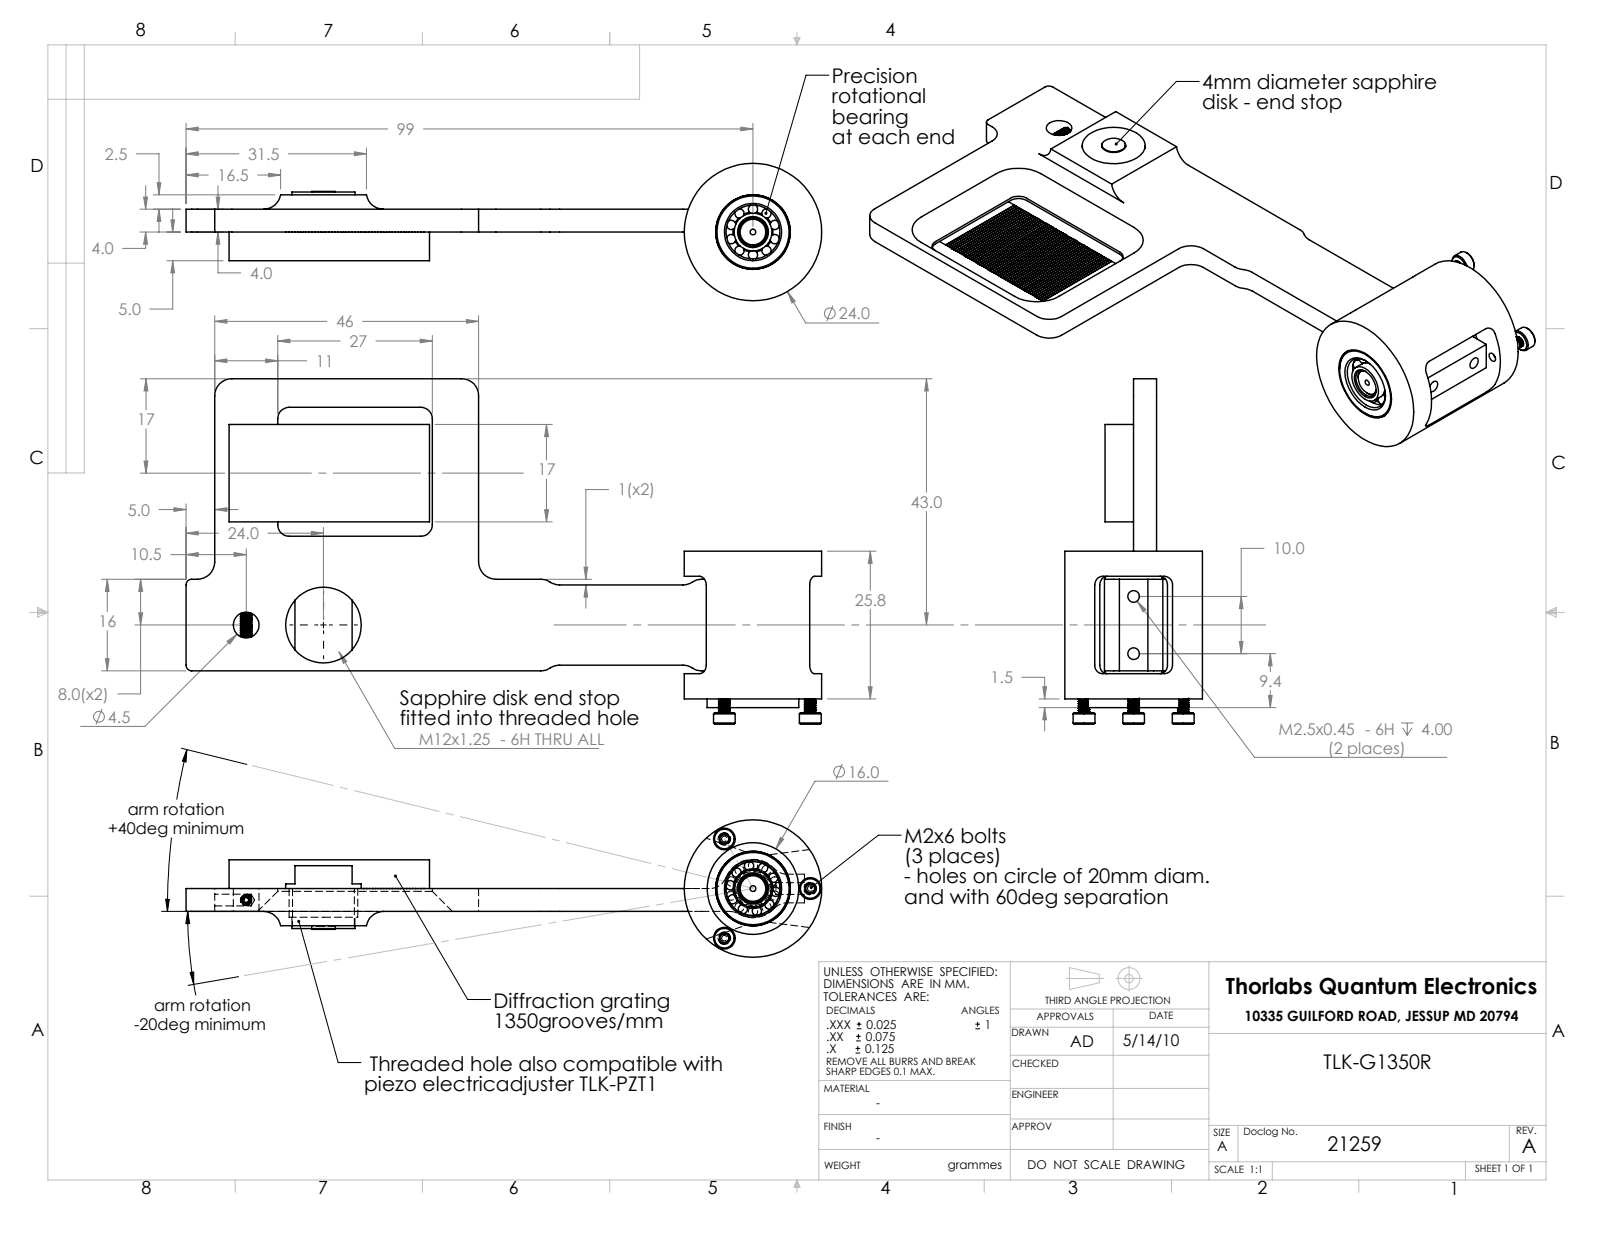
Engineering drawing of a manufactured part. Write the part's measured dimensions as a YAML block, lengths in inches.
part_name: "21259 (TLK-G1350R)"
step_written_by: "SolidWorks 2009 (AUTOMOTIVE_DESIGN)"
units: inches
bodies: {solids: 0, faces: 636, planar: 147, cylindrical: 324, other: 165}
overall_size: [4.37, 2.374, 0.945]
round_holes:
  - {diameter: 0.081, count: 3}
  - {diameter: 0.087, count: 3}
  - {diameter: 0.063, count: 2}
  - {diameter: 0.039, count: 1}
  - {diameter: 0.165, count: 1}
  - {diameter: 0.177, count: 1}
  - {diameter: 0.197, count: 1}
  - {diameter: 0.37, count: 1}
  - {diameter: 0.513, count: 1}
round_bosses_or_shafts:
  - {diameter: 0.067, count: 10}
  - {diameter: 0.079, count: 4}
  - {diameter: 0.15, count: 3}
  - {diameter: 0.058, count: 3}
  - {diameter: 0.945, count: 1}
  - {diameter: 0.63, count: 1}
  - {diameter: 0.52, count: 1}
  - {diameter: 0.433, count: 1}
partial_cylinders:
  - {radius: 0.118, count: 18}
  - {radius: 0.059, count: 8}
  - {radius: 0.079, count: 4}
  - {radius: 0.039, count: 2}
  - {radius: 0.033, count: 1}
  - {radius: 0.201, count: 1}
face_to_face_distances: [0.157, 0.197, 0.354, 0.823, 0.098, 0.193, 0.059, 0.843, 0.02, 0.173]
hole_center_spacings: [0.394, 0.682, 0.531, 0.919, 1.311, 3.298, 3.314, 3.485]
